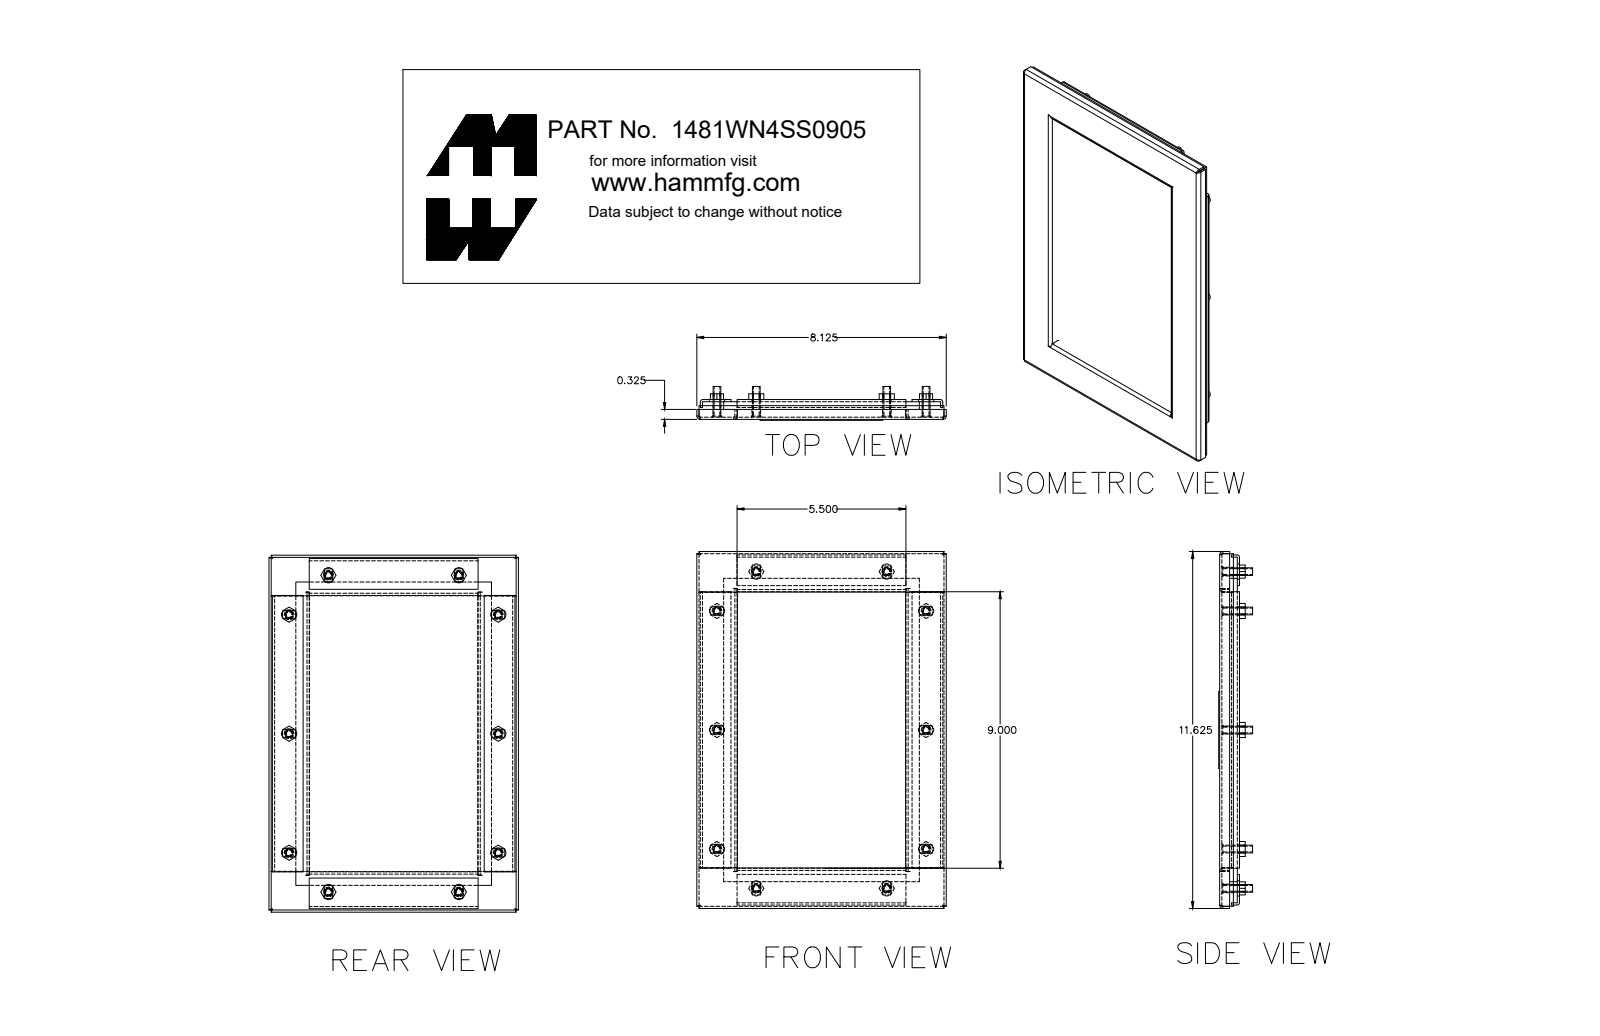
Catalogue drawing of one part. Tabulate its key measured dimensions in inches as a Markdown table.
| quantity | value |
| --- | --- |
| part name | 1481WN4SS0905_Default |
| STEP written by | SolidWorks 2019 (CONFIG_CONTROL_DESIGN) |
| units | inches |
| bodies | 27 solids, 336 faces (224 planar, 104 cylindrical, 8 other) |
| overall size | 12.025 × 8.525 × 1.072 |
| volume | 27.37 in³ |
| surface area | 468.6 in² |
| round holes (diameter × count) | 0.196 × 10, 0.328 × 10 |
| round bosses / shafts (diameter × count) | 0.313 × 10, 0.25 × 10 |
| partial cylindrical surfaces (radius × count) | 0.036 × 8, 0.108 × 8, 0.016 × 4, 0.088 × 4 |
| main face-to-face distances | 0.072, 0.575, 0.503, 0.325, 0.253, 0.25, 0.575, 0.647, 0.322, 0.072 |
| hole center spacings | 6.813, 7.837, 10.313, 5.313, 7.838, 9.122, 1.812, 3.875 |
